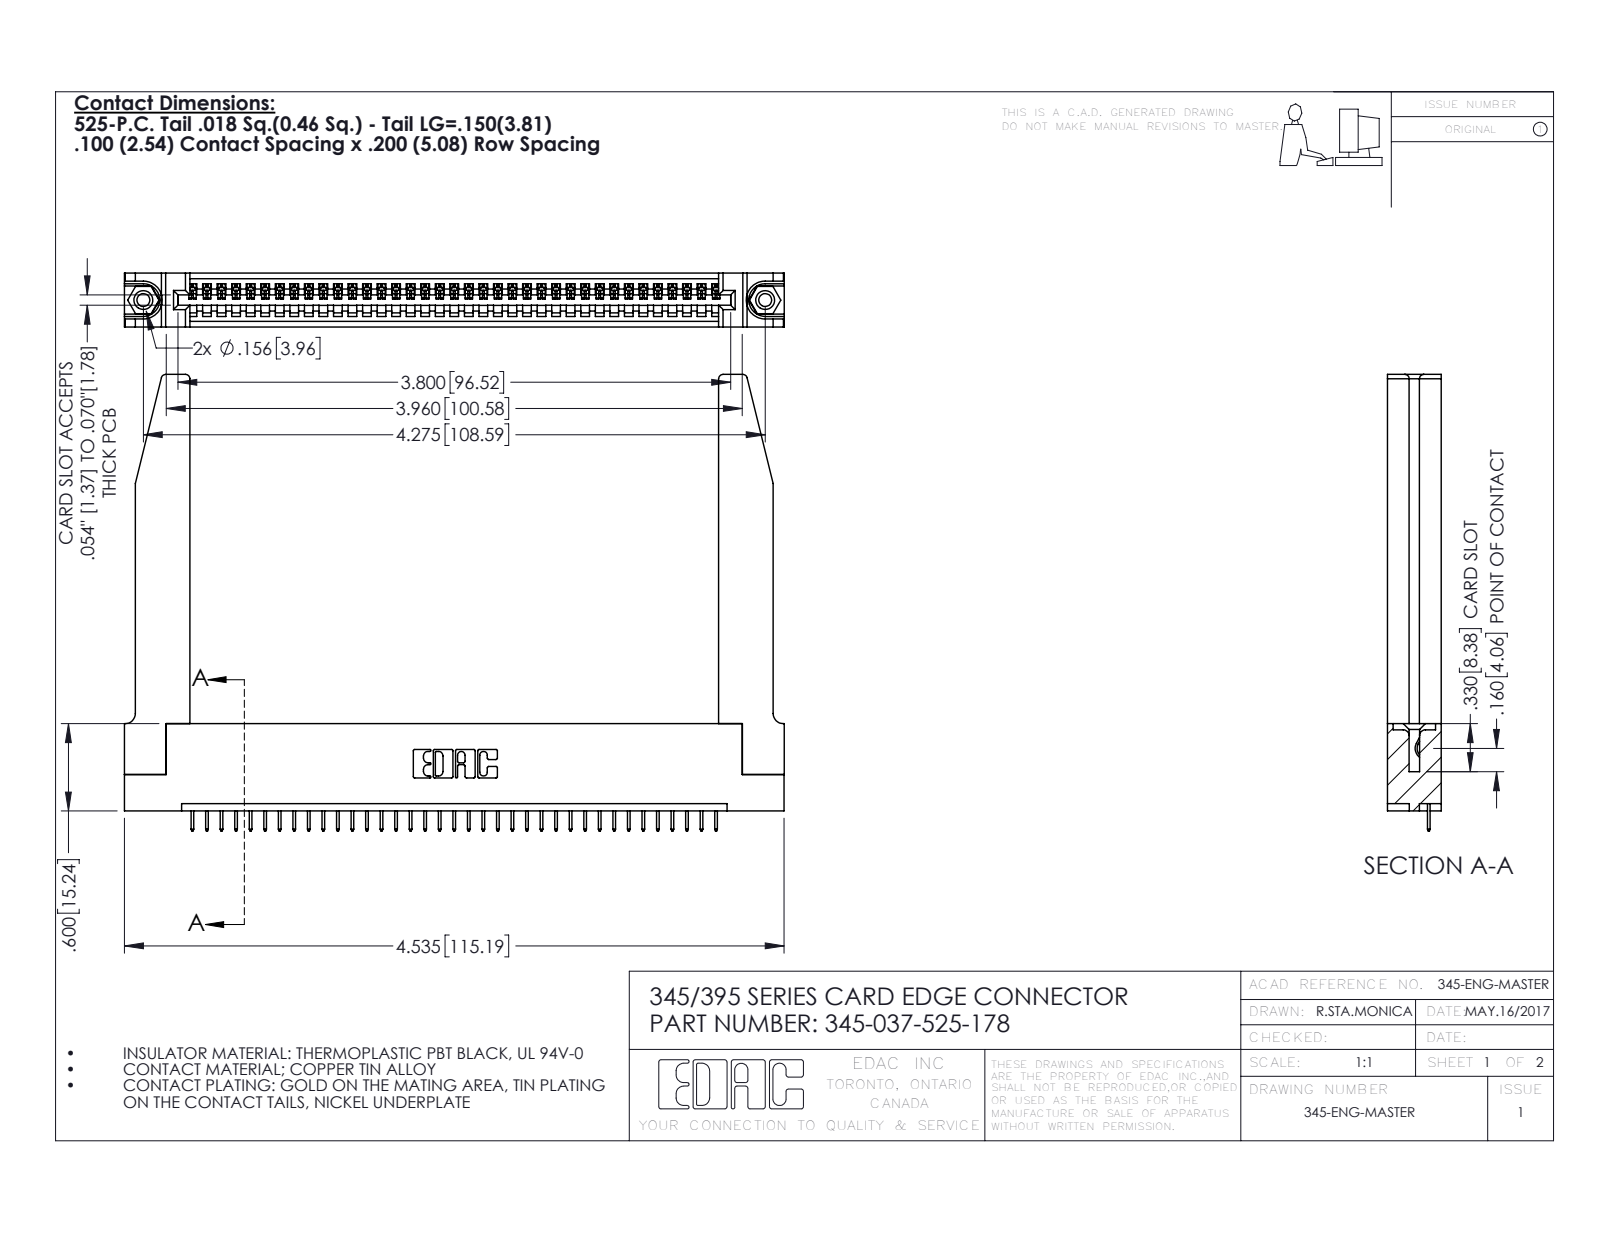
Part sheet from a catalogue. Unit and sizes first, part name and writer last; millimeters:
Units: millimetres
Overall size (bounding box): 115.2 × 79.7 × 9.4
Round holes (diameter × count): ⌀2.3 ×2, ⌀3.2 ×2, ⌀4 ×2, ⌀1.6 ×1
Round bosses / shafts (diameter × count): ⌀3.9 ×2
Partial cylindrical surfaces — rounded edges, fillets, slot ends (radius × count): R0.2 ×74, R0.3 ×22, R0.8 ×8, R0.2 ×6, R0.8 ×6, R0.7 ×3, R0.8 ×2, R1 ×2
Main face-to-face distances: 9.4, 1.8, 7.6, 5.1, 2.5, 6.9, 0.6, 5.7, 3.8, 3.8
Hole centre spacings: 6.9, 102.6, 108.6
Volume: 18 520 mm³ · Surface area: 20 560 mm²
Bodies: 42 solids, 2654 faces (1924 planar, 678 cylindrical, 52 other)
Part name (STEP PRODUCT): 345 Part_Flush Mounting Lugs - 0.156 Dia-TH; 345-220-078_345-220-078; 345-037-525-178; 345-292-001_345-293-125 (+1 more)
STEP written by: SolidWorks 2020 (CONFIG_CONTROL_DESIGN)
